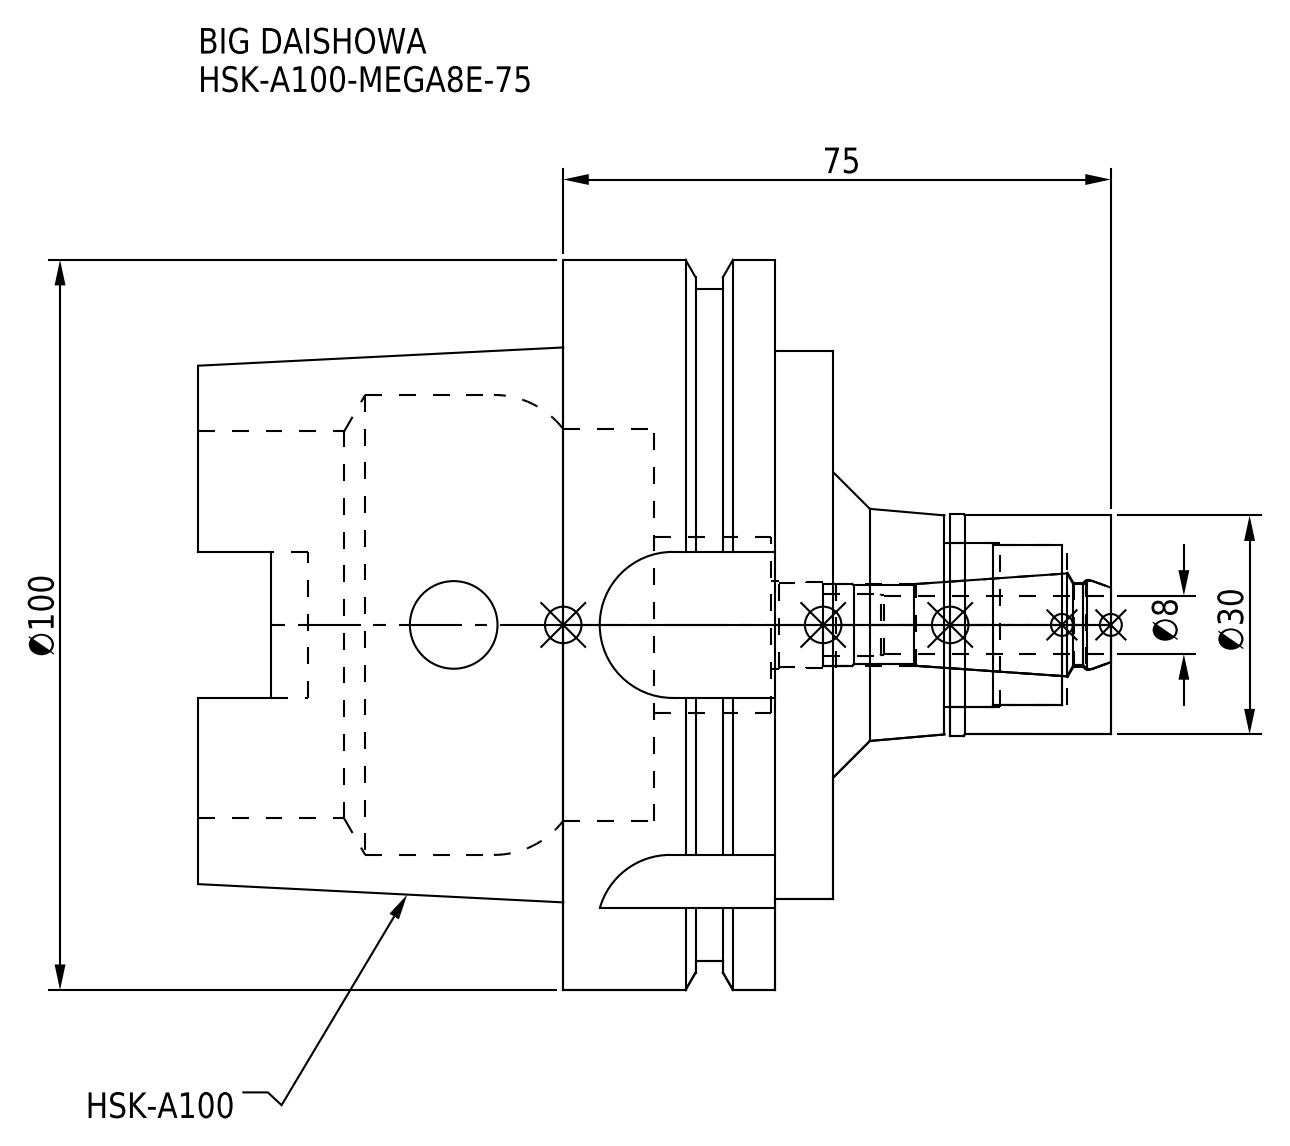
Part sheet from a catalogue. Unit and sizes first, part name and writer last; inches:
Units: inches
Overall size (bounding box): 4.921 × 3.937 × 3.937
Round holes (diameter × count): ⌀0.472 ×2, ⌀0.441 ×1, ⌀0.449 ×1, ⌀0.453 ×1, ⌀0.465 ×1, ⌀0.484 ×1, ⌀0.866 ×1, ⌀0.886 ×1, ⌀0.945 ×1, ⌀2.087 ×1, ⌀2.118 ×1, ⌀2.48 ×1
Round bosses / shafts (diameter × count): ⌀3.937 ×1, ⌀3.622 ×1, ⌀2.953 ×1, ⌀1.193 ×1, ⌀1.181 ×1
Partial cylindrical surfaces — rounded edges, fillets, slot ends (radius × count): R0.192 ×4, R0.394 ×4
Main face-to-face distances: 1.142, 0.315, 1.457, 0.967, 0.652, 0.49, 3.425, 3.11, 2.459, 1.969
Volume: 19.06 in³ · Surface area: 93.11 in²
Bodies: 2 solids, 126 faces (42 planar, 56 cylindrical, 28 other)
Part name (STEP PRODUCT): DXF_TEMP_ASSY_ASM_4_ASM.stp; MEN8_1.stp; HSK-A100-MEGA8E-75-080-FreeParts; HSK-A100-MEGA8E-75_1.stp (+3 more)
STEP written by: SolidWorks 2019 (CONFIG_CONTROL_DESIGN)
